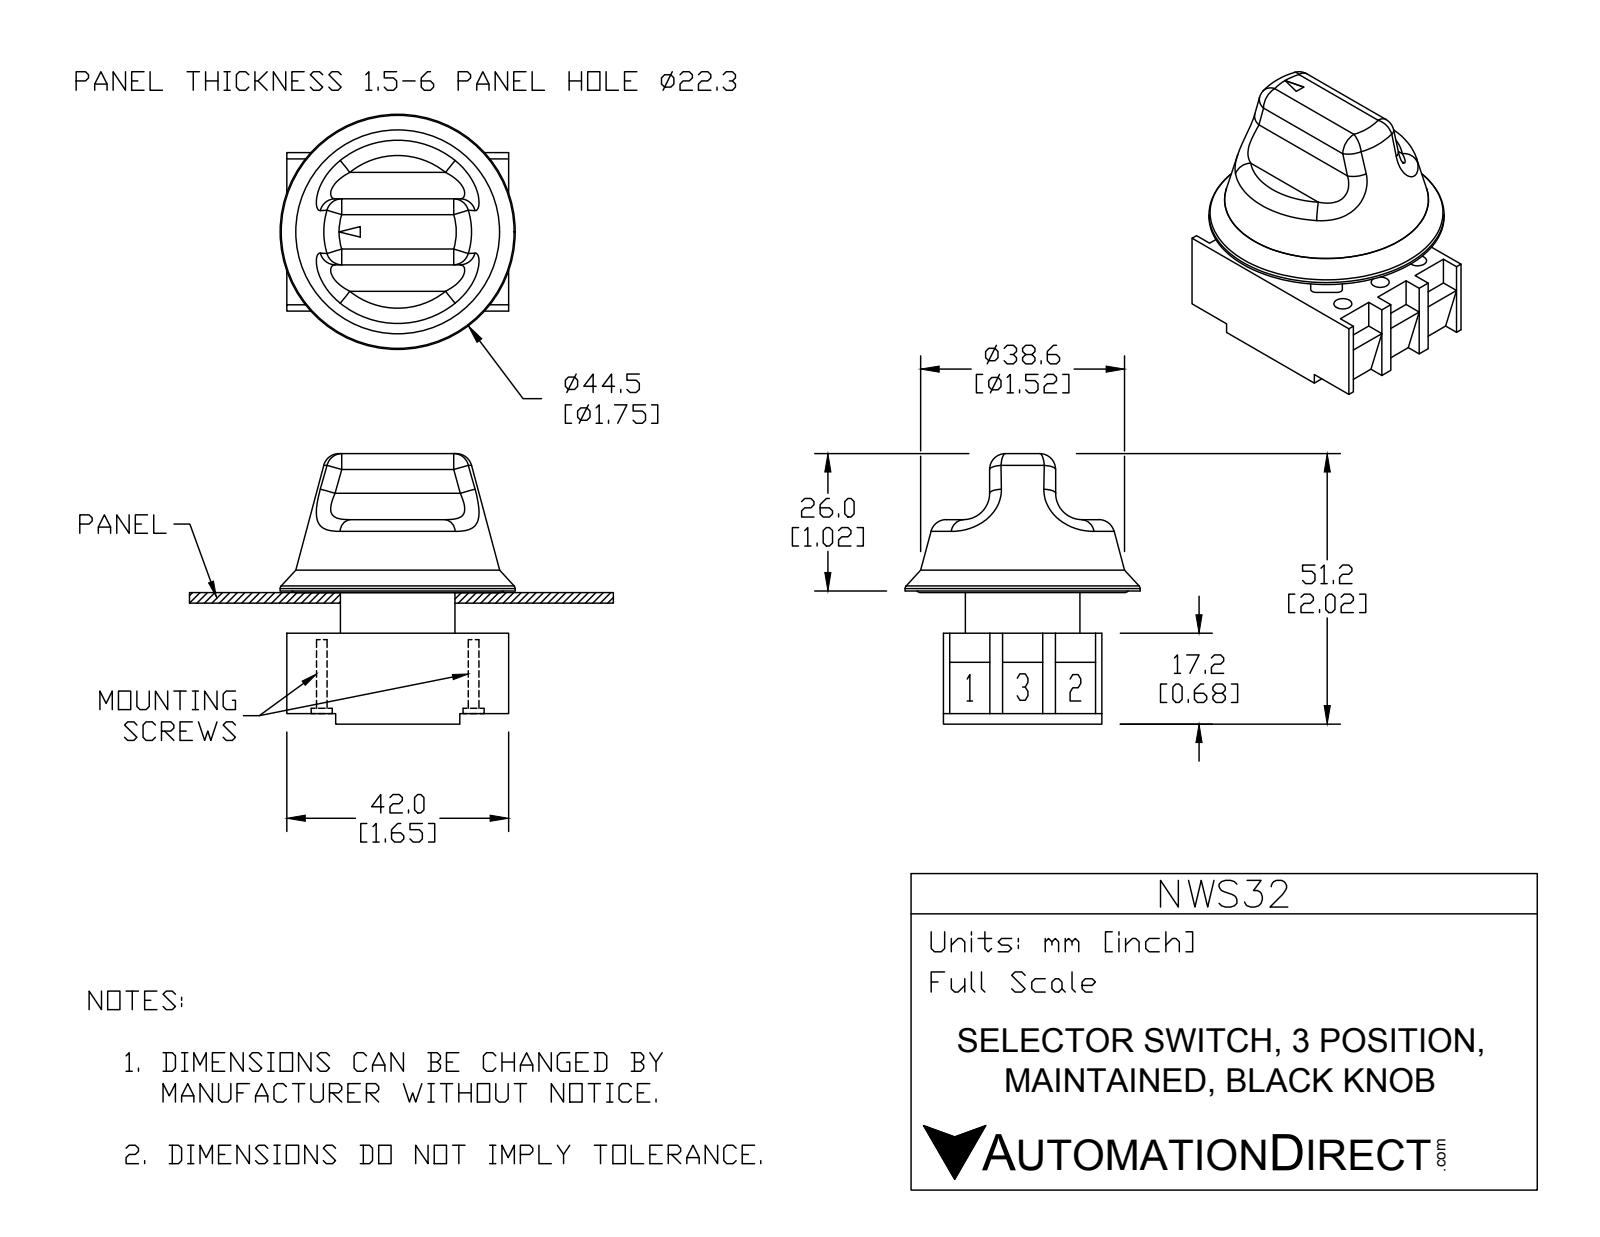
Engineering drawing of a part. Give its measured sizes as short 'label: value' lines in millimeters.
name: NWS32
written by: SolidWorks 2015 (AUTOMOTIVE_DESIGN)
unit: mm
bodies: 7 solids, 236 faces (134 planar, 67 cylindrical, 35 other)
size: 51.2 × 44.5 × 44.5
volume: 35 027 mm³; area: 19 099 mm²
holes: 6× ⌀3.4, 6× ⌀5, 1× ⌀12.5
bosses: 2× ⌀4.6, 2× ⌀4, 1× ⌀44.5, 1× ⌀21.7
rounds: 8× R1, 5× R8.7, 2× R3, 2× R5, 1× R11
face distances: 3.95, 30, 8, 11.95, 7.7, 4.25, 10, 15.2, 22.9, 23.2
hole spacings: 10, 17.52, 30.45, 28.76, 14.38, 20, 35.03
